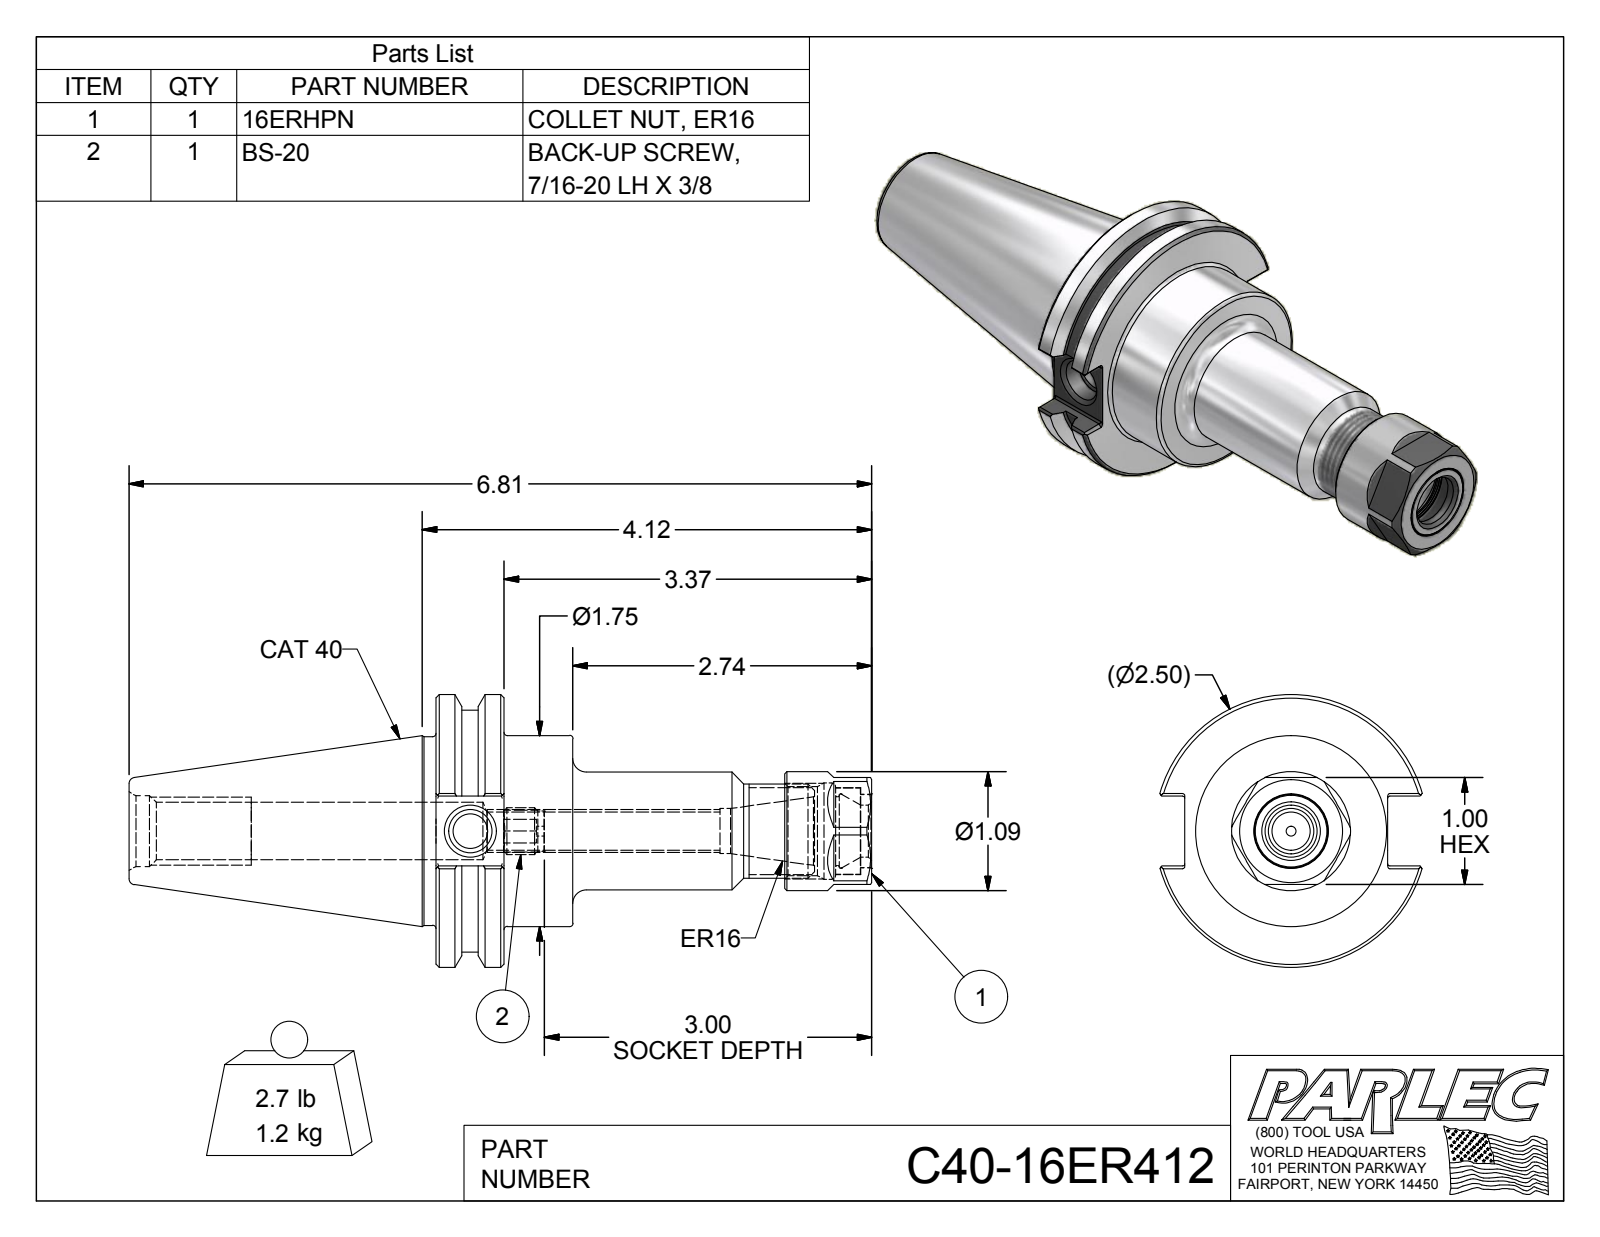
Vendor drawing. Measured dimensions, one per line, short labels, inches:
name: C40-16ER412; C40-16ER4-1; 16ERHPN; BS-20
written by: Autodesk Inventor 2012 (AUTOMOTIVE_DESIGN)
unit: in
bodies: 4 solids, 145 faces (62 planar, 42 cylindrical, 41 other)
size: 6.808 × 2.5 × 2.403
volume: 9.497 in³; area: 53.27 in²
holes: 1× ⌀0.09, 1× ⌀0.315, 1× ⌀0.351, 1× ⌀0.399, 1× ⌀0.413, 1× ⌀0.474, 1× ⌀0.527, 1× ⌀0.527, 1× ⌀0.63, 1× ⌀0.648, 1× ⌀0.674, 1× ⌀0.68
bosses: 1× ⌀2.5, 1× ⌀2.219, 1× ⌀1.75, 1× ⌀1.73, 1× ⌀1.092, 1× ⌀1.08, 1× ⌀0.866, 1× ⌀0.79
rounds: 12× R0.02
face distances: 0.625, 1.255, 0.63, 0.98, 3.995, 3.37, 2.74, 0.17, 0.81, 3.199
